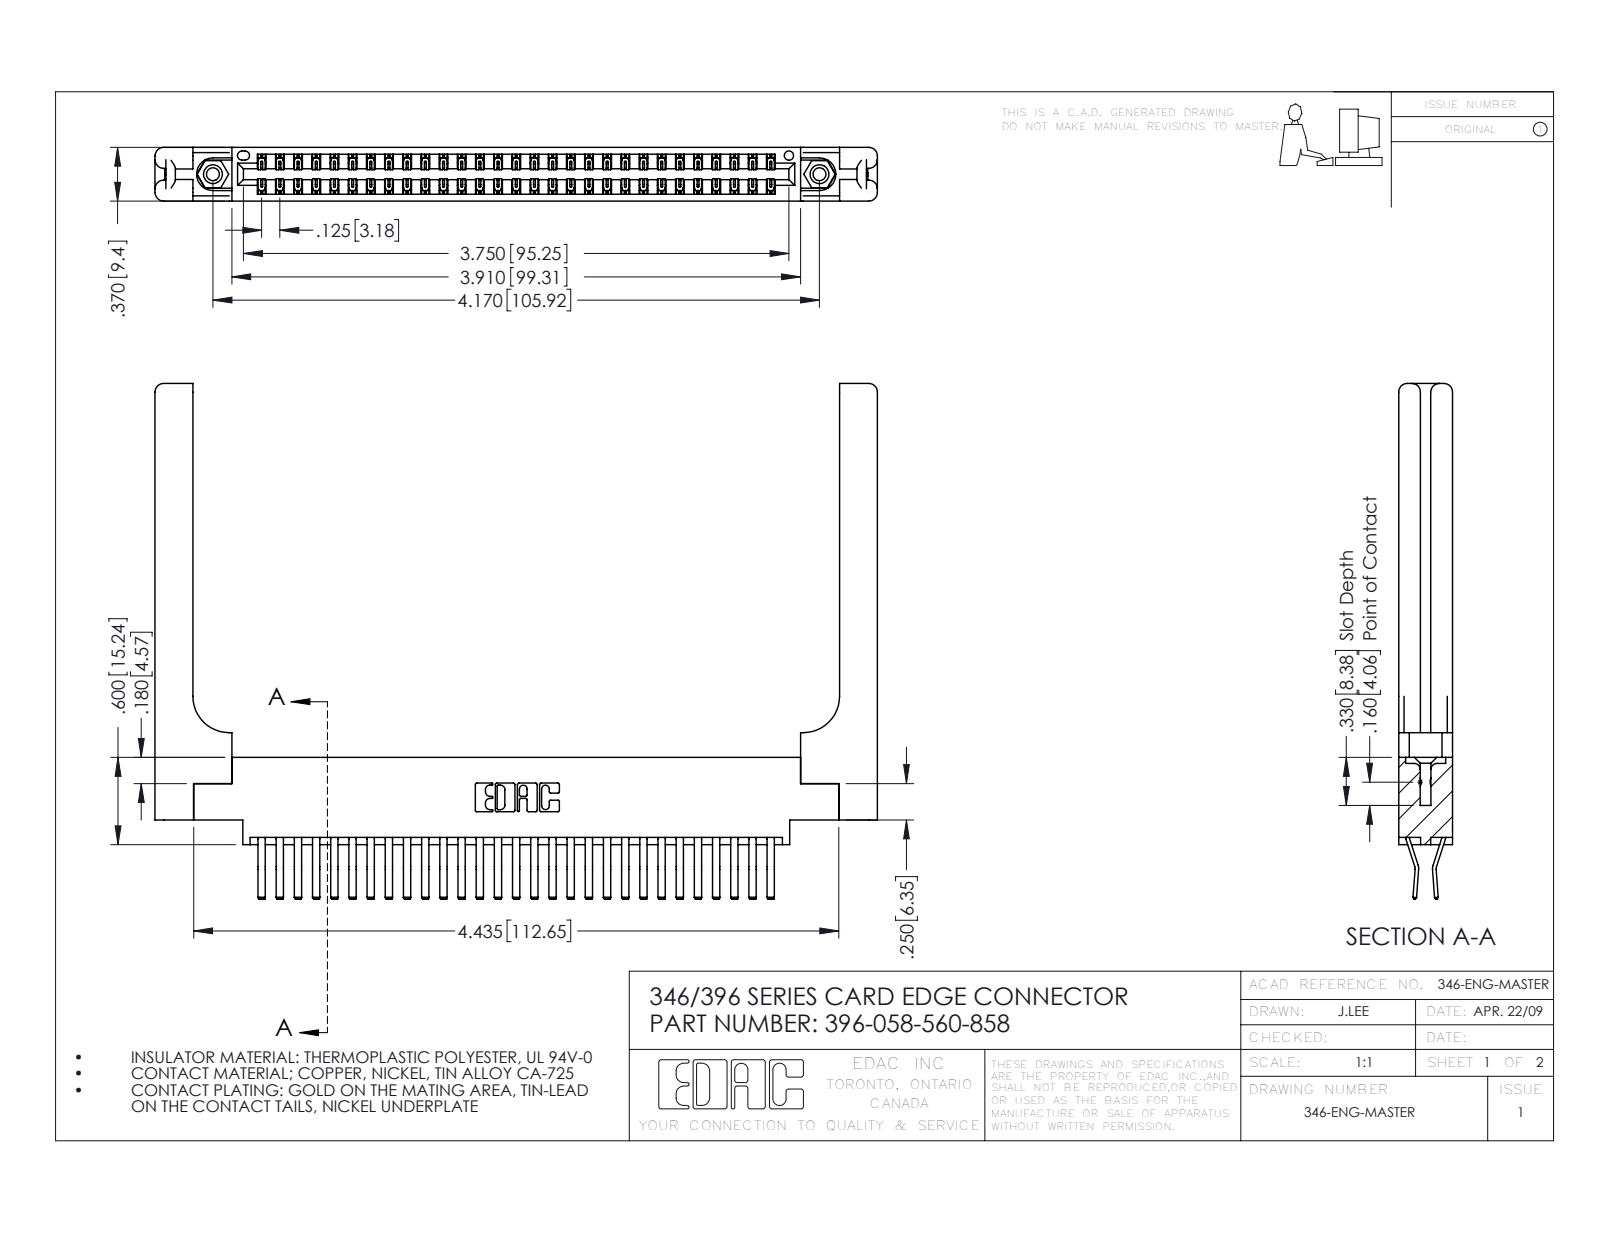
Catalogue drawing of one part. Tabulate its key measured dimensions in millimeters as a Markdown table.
| quantity | value |
| --- | --- |
| part name | 396-058-560-858; 345-250-001_345-250-001-102; 345-292-001_560 Tail; 346 Part_0.170 Offset - 0.156 Dia-TH (+1 more) |
| STEP written by | SolidWorks 2016 (CONFIG_CONTROL_DESIGN) |
| units | millimeters |
| bodies | 63 solids, 3514 faces (2258 planar, 1196 cylindrical, 60 other) |
| overall size | 126.1 × 90 × 9.4 |
| volume | 19 930 mm³ |
| surface area | 23 040 mm² |
| round holes (diameter × count) | 2.3 × 2, 3.2 × 2, 4 × 2, 1.6 × 1 |
| round bosses / shafts (diameter × count) | 3.9 × 2 |
| partial cylindrical surfaces (radius × count) | 0.2 × 87, 0.3 × 22, 1.5 × 16, 0.2 × 6, 0.8 × 6, 0.7 × 3, 0.3 × 2, 0.4 × 2 |
| main face-to-face distances | 9.4, 1.2, 8.2, 1.8, 3.8, 3.8, 0.6, 6.4, 7.6, 7 |
| hole center spacings | 6.2, 100.6, 105.9 |
